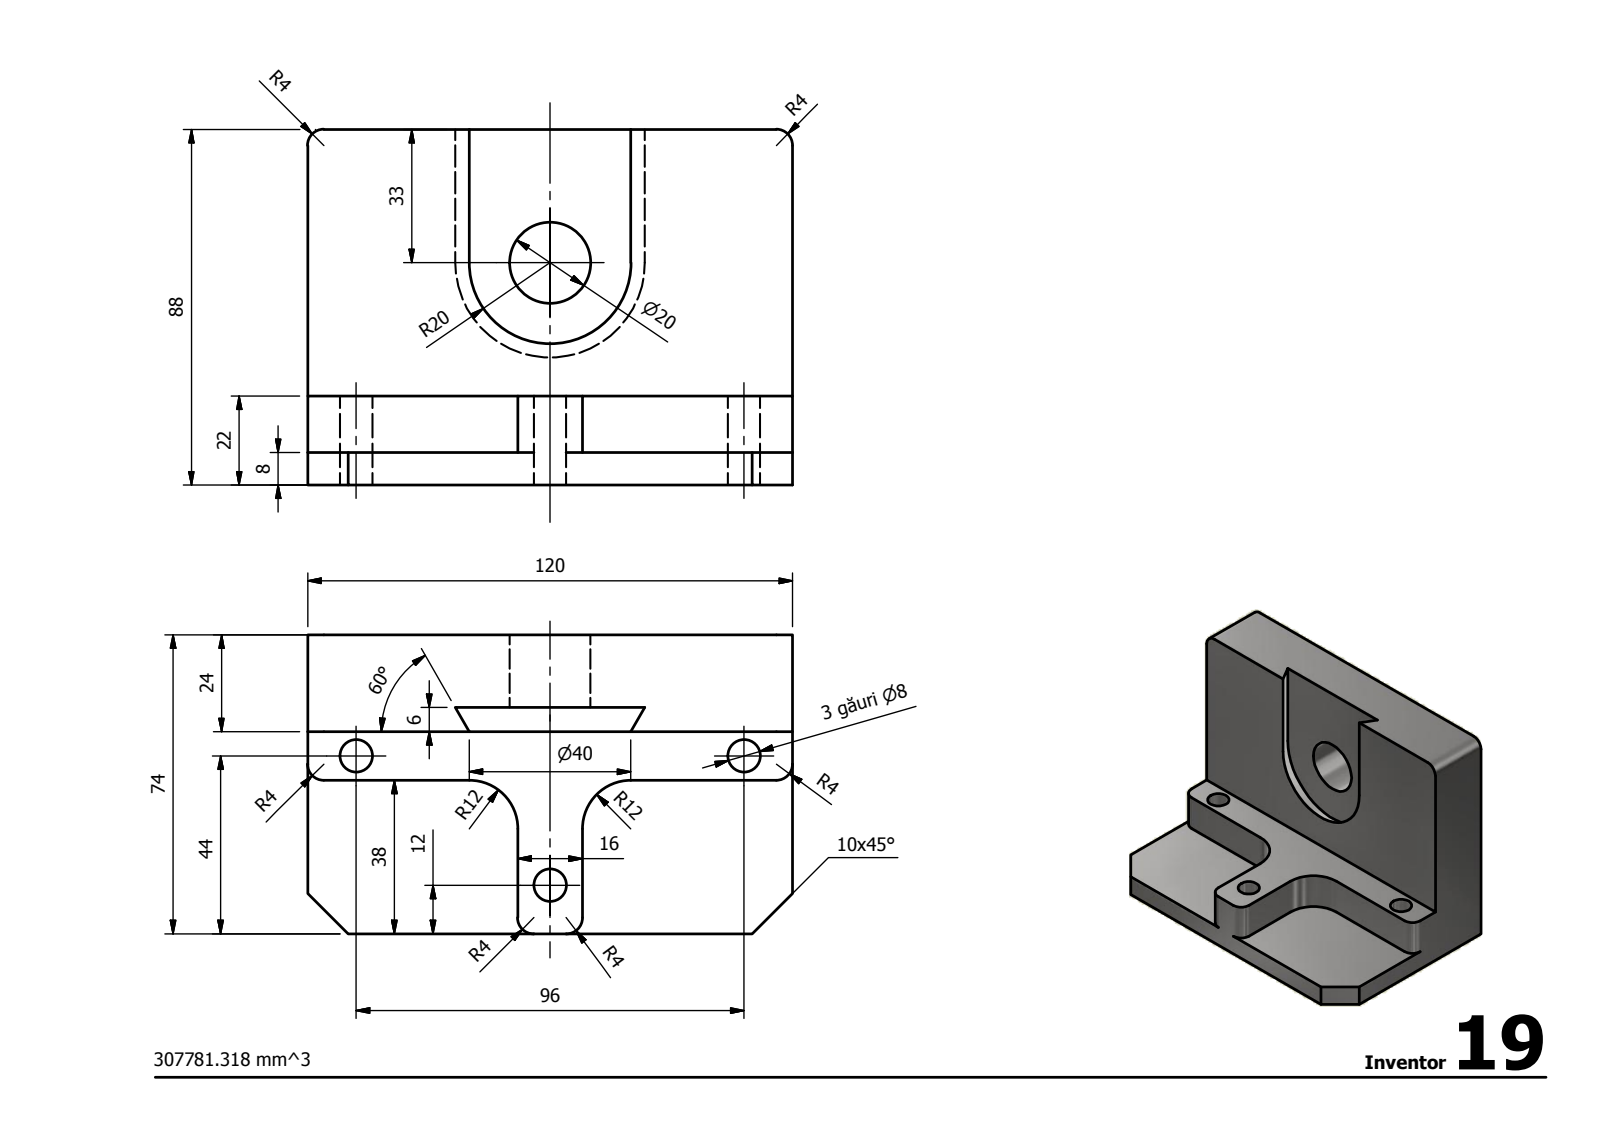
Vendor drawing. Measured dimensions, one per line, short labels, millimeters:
written by: Autodesk Inventor 2014 (AUTOMOTIVE_DESIGN)
unit: mm
bodies: 1 solid, 32 faces (19 planar, 12 cylindrical, 1 other)
size: 120 × 88 × 74
volume: 307 781 mm³; area: 47 668 mm²
holes: 3× ⌀8, 1× ⌀20
rounds: 6× R4, 2× R12
face distances: 24, 8, 18, 120, 88, 80, 6, 22, 14, 66
hole spacings: 57.69, 96
